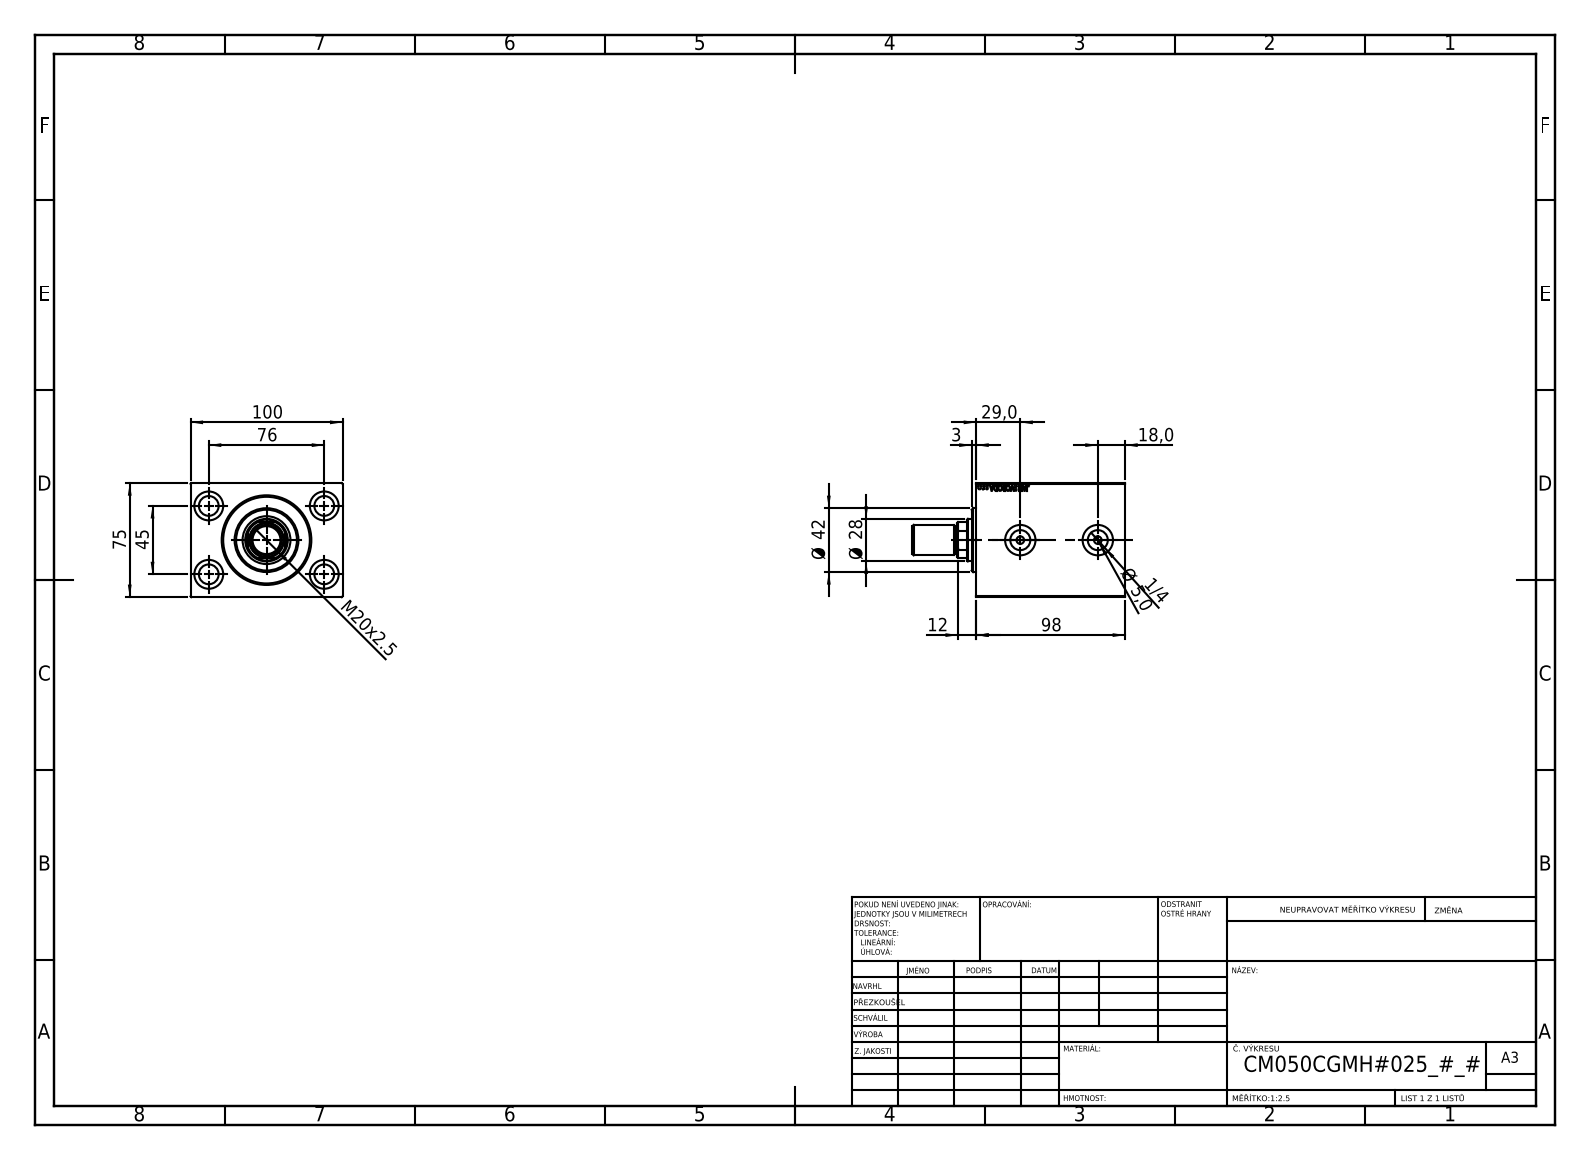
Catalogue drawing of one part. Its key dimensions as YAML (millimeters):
part_name: "V450CM_VC_B; V450CM_MALE_METRIC; V450CM_C_VCP; V450CM_C_Body"
step_written_by: "SolidWorks 2019 (CONFIG_CONTROL_DESIGN)"
units: millimeters
bodies: {solids: 4, faces: 879, planar: 413, cylindrical: 66, other: 400}
overall_size: [140, 100, 75]
volume: 640252
surface_area: 108254
round_holes:
  - {diameter: 13, count: 4}
  - {diameter: 19, count: 4}
  - {diameter: 5, count: 2}
  - {diameter: 13.16, count: 2}
  - {diameter: 20, count: 2}
  - {diameter: 18.5, count: 1}
  - {diameter: 28, count: 1}
  - {diameter: 31.5, count: 1}
  - {diameter: 50, count: 1}
  - {diameter: 52, count: 1}
  - {diameter: 57, count: 1}
round_bosses_or_shafts:
  - {diameter: 42, count: 1}
  - {diameter: 20, count: 1}
  - {diameter: 18, count: 1}
partial_cylinders:
  - {radius: 13.5, count: 1}
face_to_face_distances: [75, 100, 98, 84, 14, 12, 72, 25, 86, 47]
hole_center_spacings: [44.16, 45, 76, 88.32, 51]
